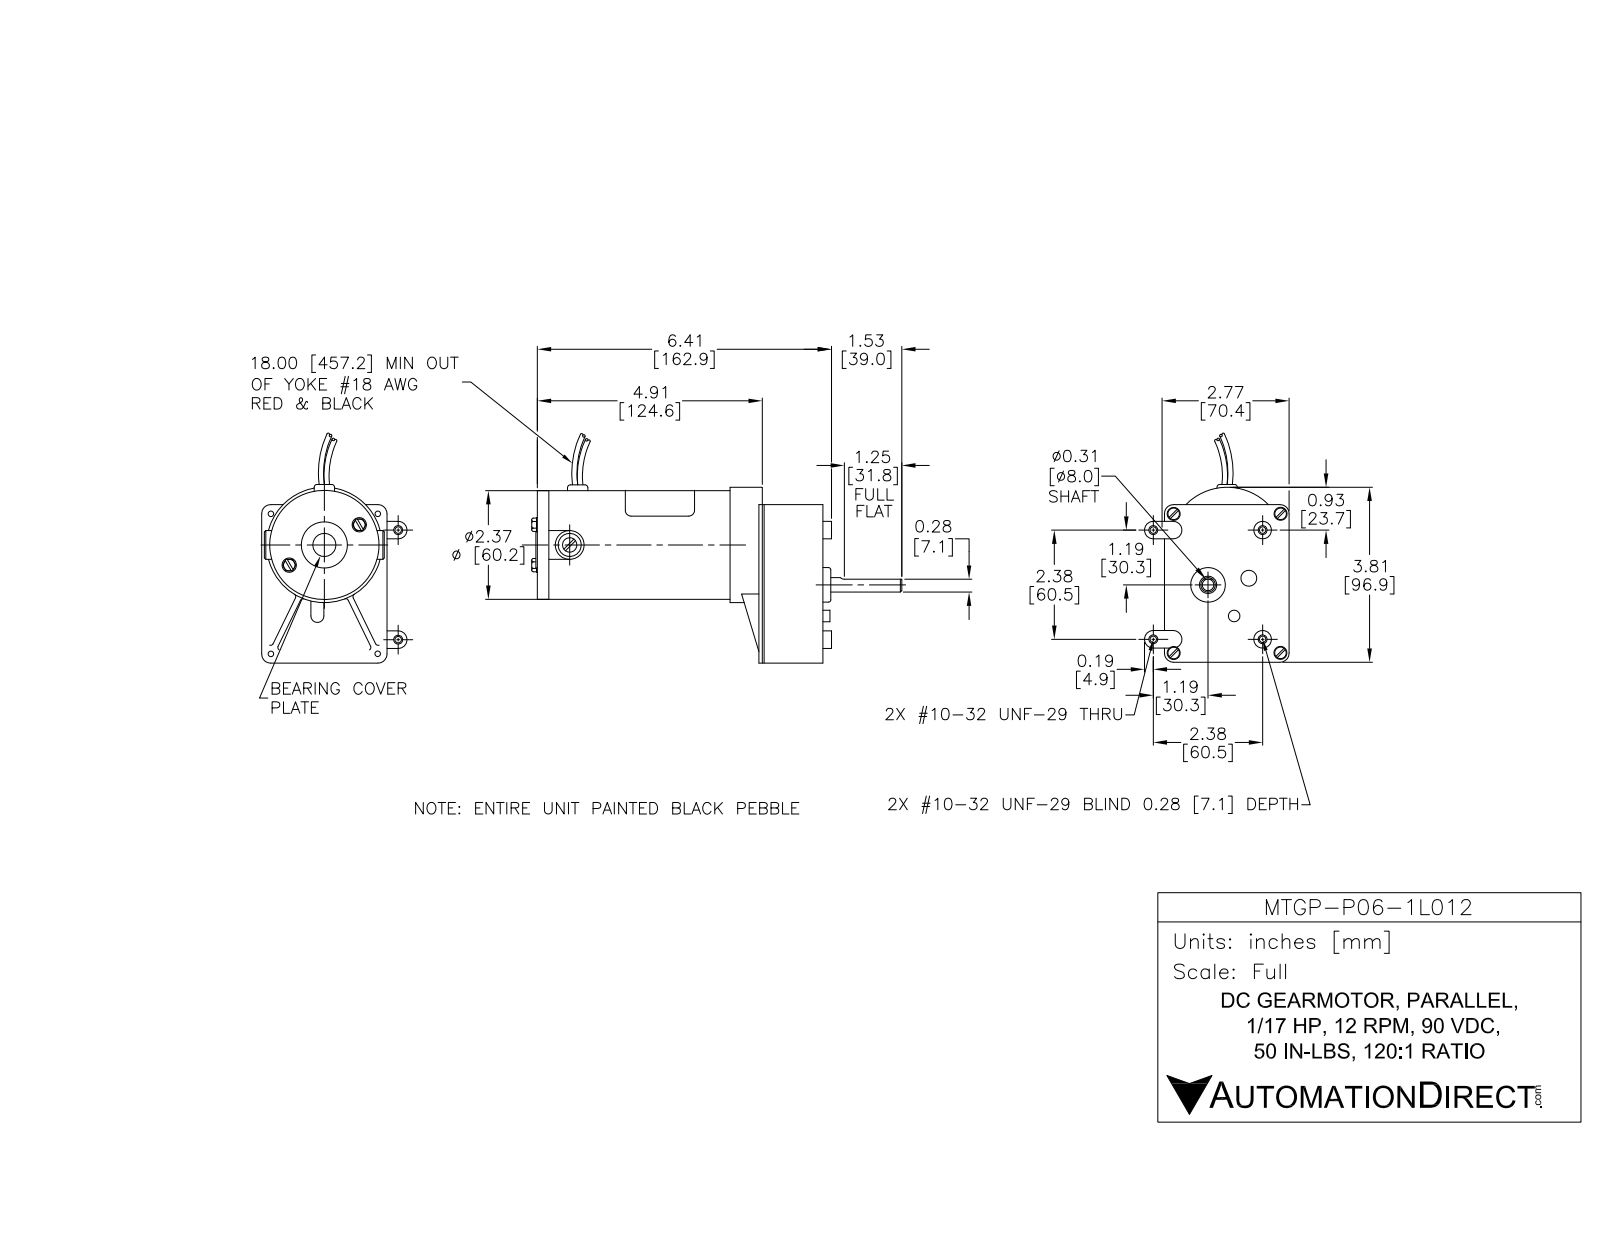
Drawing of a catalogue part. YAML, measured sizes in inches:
part_name: "MTGP-P06-1L012"
step_written_by: "SolidWorks 2016 (AUTOMOTIVE_DESIGN)"
units: inches
bodies: {solids: 27, faces: 266, planar: 115, cylindrical: 130, other: 21}
overall_size: [7.922, 5.092, 3.181]
volume: 20.18
surface_area: 156.4
round_holes:
  - {diameter: 0.194, count: 5}
  - {diameter: 0.063, count: 4}
  - {diameter: 0.283, count: 4}
  - {diameter: 0.156, count: 2}
  - {diameter: 0.25, count: 1}
  - {diameter: 0.312, count: 1}
  - {diameter: 0.562, count: 1}
  - {diameter: 1, count: 1}
  - {diameter: 2.25, count: 1}
round_bosses_or_shafts:
  - {diameter: 0.312, count: 4}
  - {diameter: 0.38, count: 2}
  - {diameter: 0.1, count: 2}
  - {diameter: 2.46, count: 1}
  - {diameter: 2.375, count: 1}
  - {diameter: 0.75, count: 1}
  - {diameter: 0.625, count: 1}
  - {diameter: 0.625, count: 1}
partial_cylinders:
  - {radius: 0.031, count: 10}
  - {radius: 0.1, count: 4}
  - {radius: 0.19, count: 4}
  - {radius: 0.25, count: 2}
  - {radius: 0.134, count: 1}
  - {radius: 0.141, count: 1}
  - {radius: 1.222, count: 1}
face_to_face_distances: [1.4, 0.25, 4.833, 6.233, 4.583, 5.983, 4.194, 3.944, 0.639, 2.039]
hole_center_spacings: [1.223, 1.729, 0.373, 0.44, 0.875, 1.306, 1.332, 1.539]
